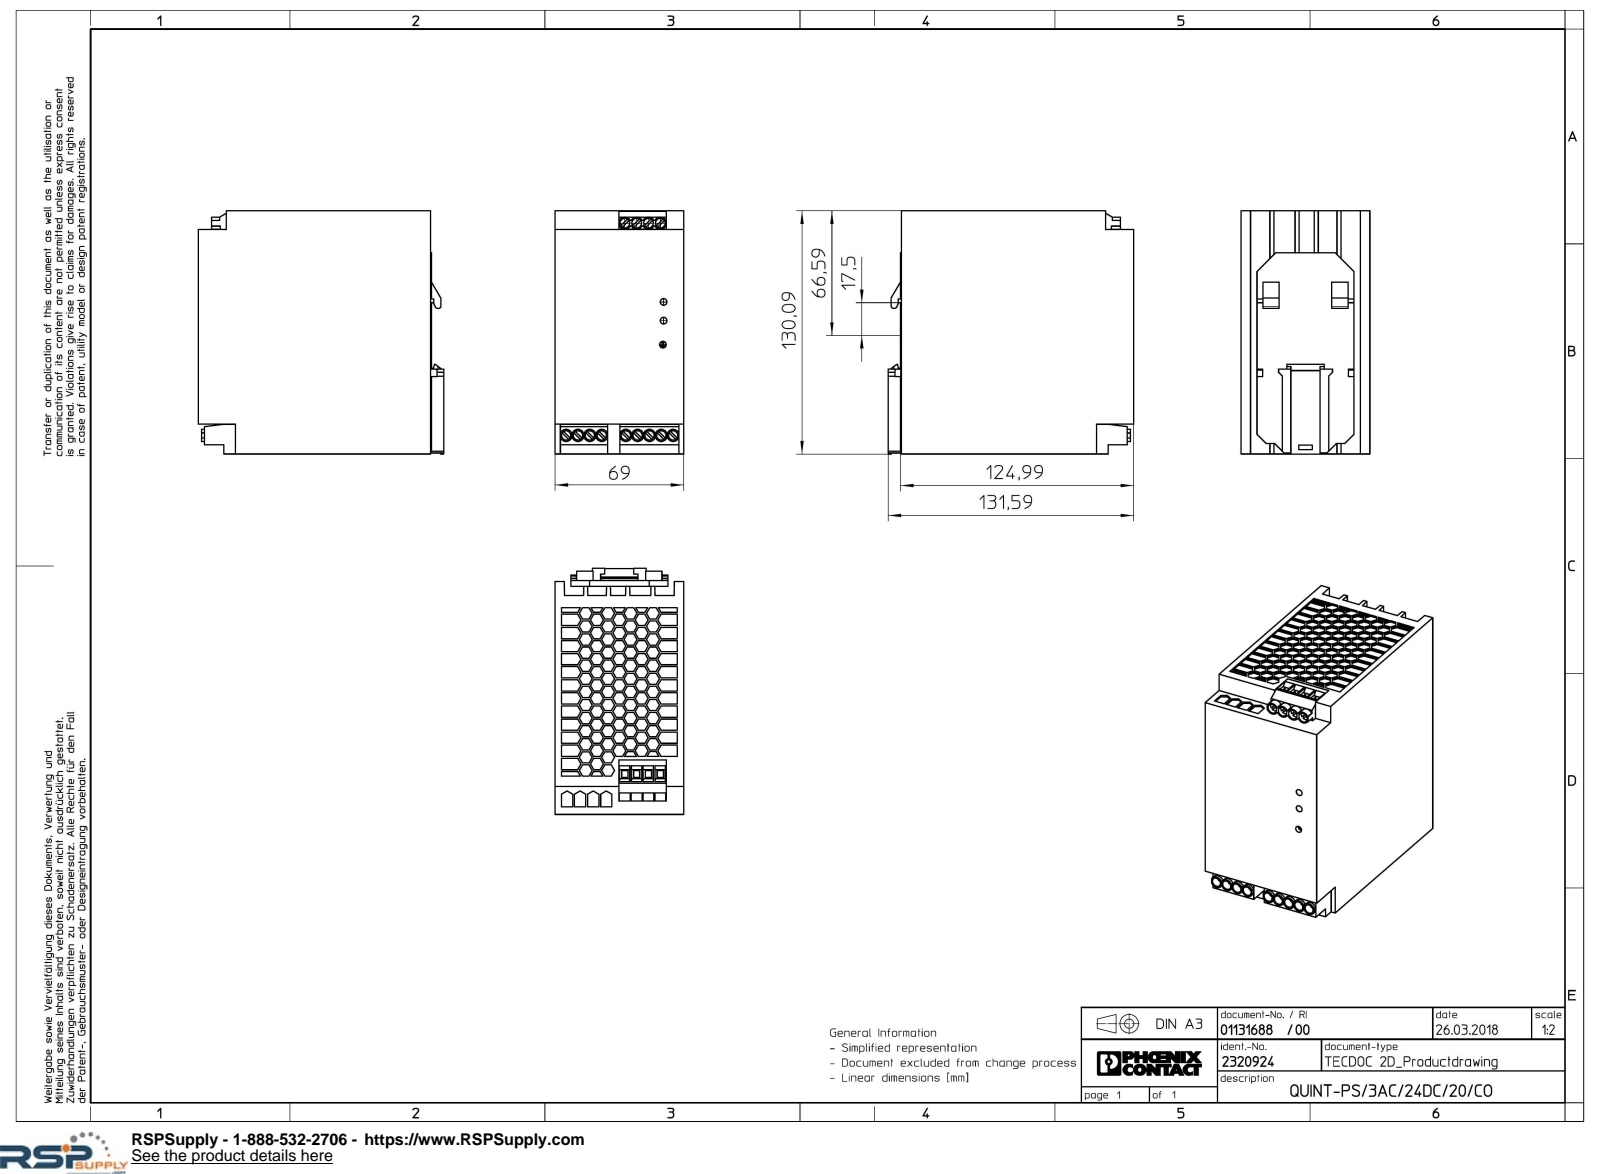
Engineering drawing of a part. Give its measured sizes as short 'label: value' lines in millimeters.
name: QUINT_PS_3AC_24DC_20_CO-select
written by: Creo Elements/Direct Modeling 20.1A 29-Sep-2018 (C) Parametric Technology GmbH (AUTOMOTIVE_DESIGN)
unit: mm
bodies: 1 solid, 2111 faces (2049 planar, 62 cylindrical, 0 other)
size: 131.59 × 130.09 × 69
volume: 1 058 000 mm³; area: 96 309 mm²
holes: 9× ⌀5, 4× ⌀5.2, 3× ⌀3.6
rounds: 13× R3.25, 2× R1
face distances: 69, 117, 0.8, 129.2, 4.99, 121.99, 3, 7.99, 124.99, 128.4
hole spacings: 6.35, 12.7, 19.05, 31.95, 38.3, 25.6, 44.65, 19.25
